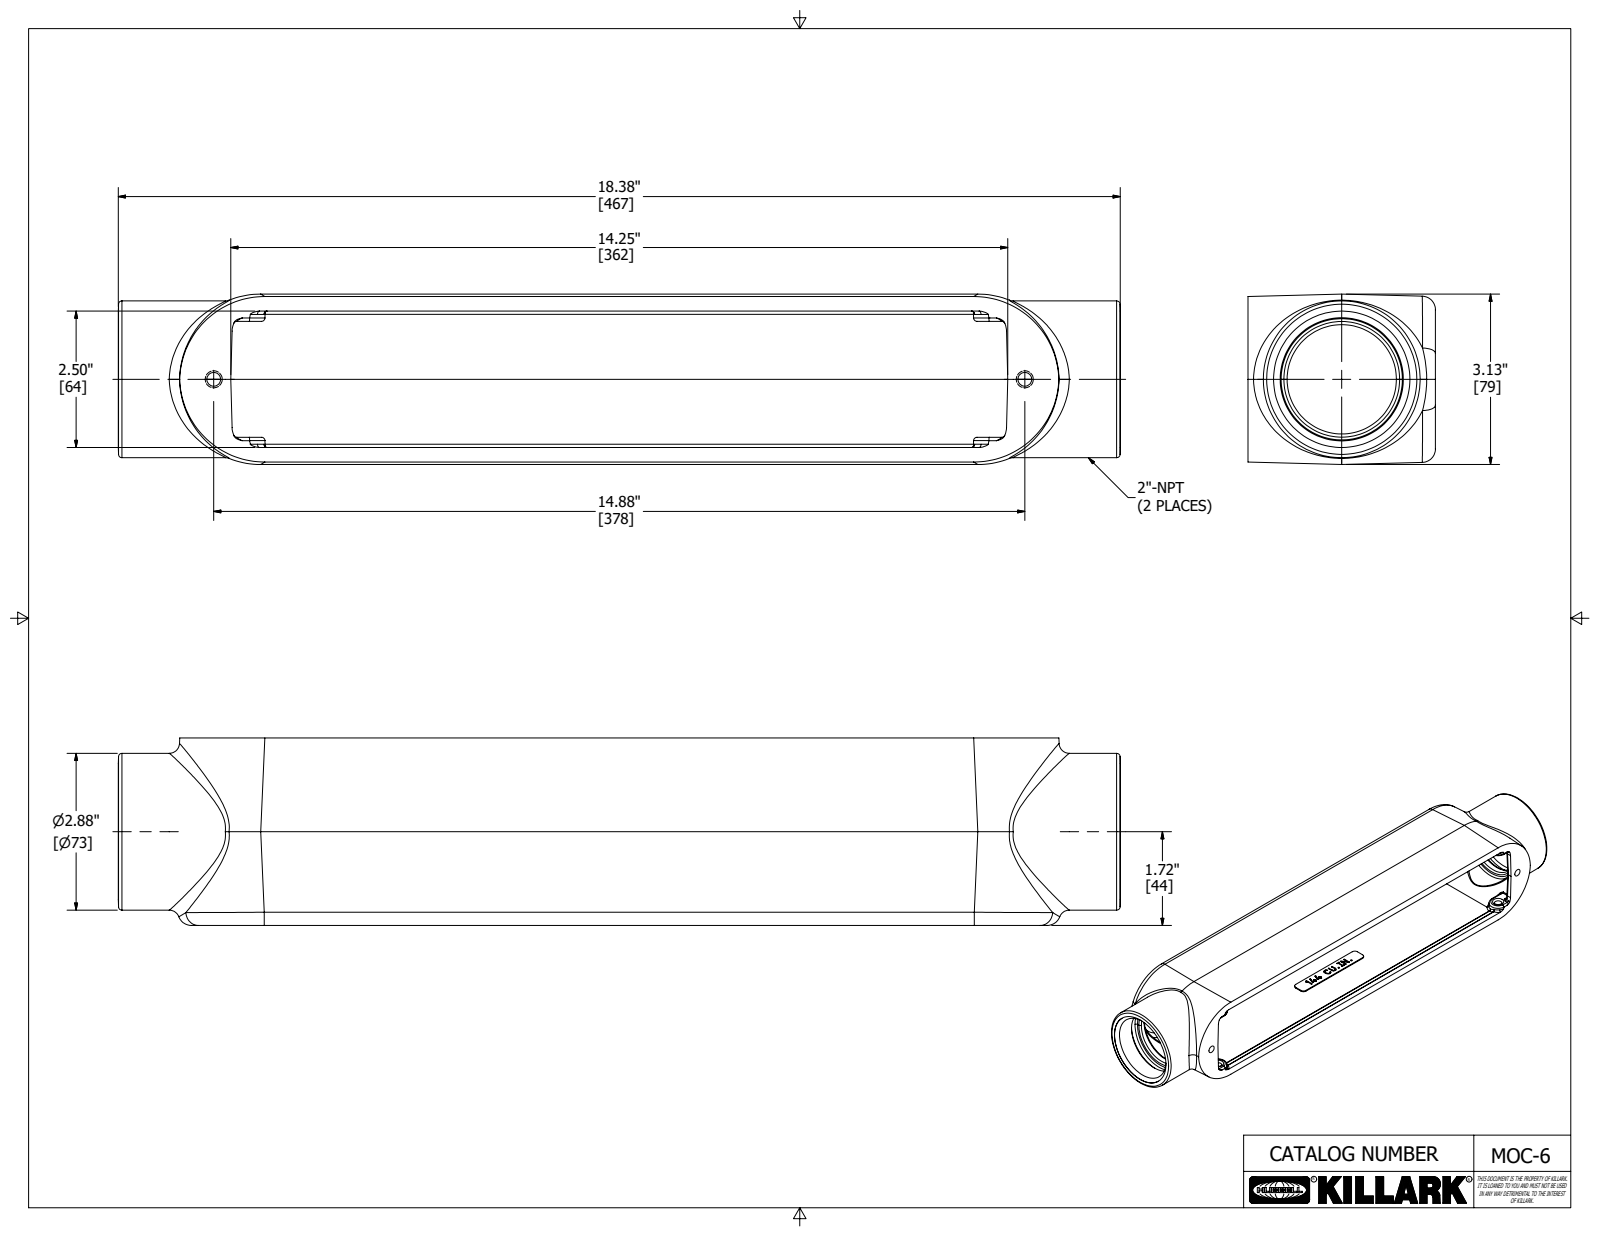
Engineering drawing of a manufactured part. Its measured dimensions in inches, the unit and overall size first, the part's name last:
Units: inches
Overall size (bounding box): 18.375 × 3.438 × 3.125
Round holes (diameter × count): ⌀0.252 ×2, ⌀2.004 ×1, ⌀2.375 ×1, ⌀2.381 ×1
Round bosses / shafts (diameter × count): ⌀2.875 ×1
Partial cylindrical surfaces — rounded edges, fillets, slot ends (radius × count): R0.062 ×20, R1.563 ×8, R0.062 ×6, R0.125 ×6, R0.375 ×4, R1.25 ×4, R0.25 ×2, R0.005 ×1
Main face-to-face distances: 3.125, 2.625, 3.438, 0.063, 2.563, 0.031, 3.406, 2.5, 3, 0.25
Hole centre spacings: 14.875
Volume: 43.85 in³ · Surface area: 362.2 in²
Bodies: 1 solid, 661 faces (278 planar, 71 cylindrical, 312 other)
Part name (STEP PRODUCT): 21238-2
STEP written by: Autodesk Inventor 2020 (AUTOMOTIVE_DESIGN)
